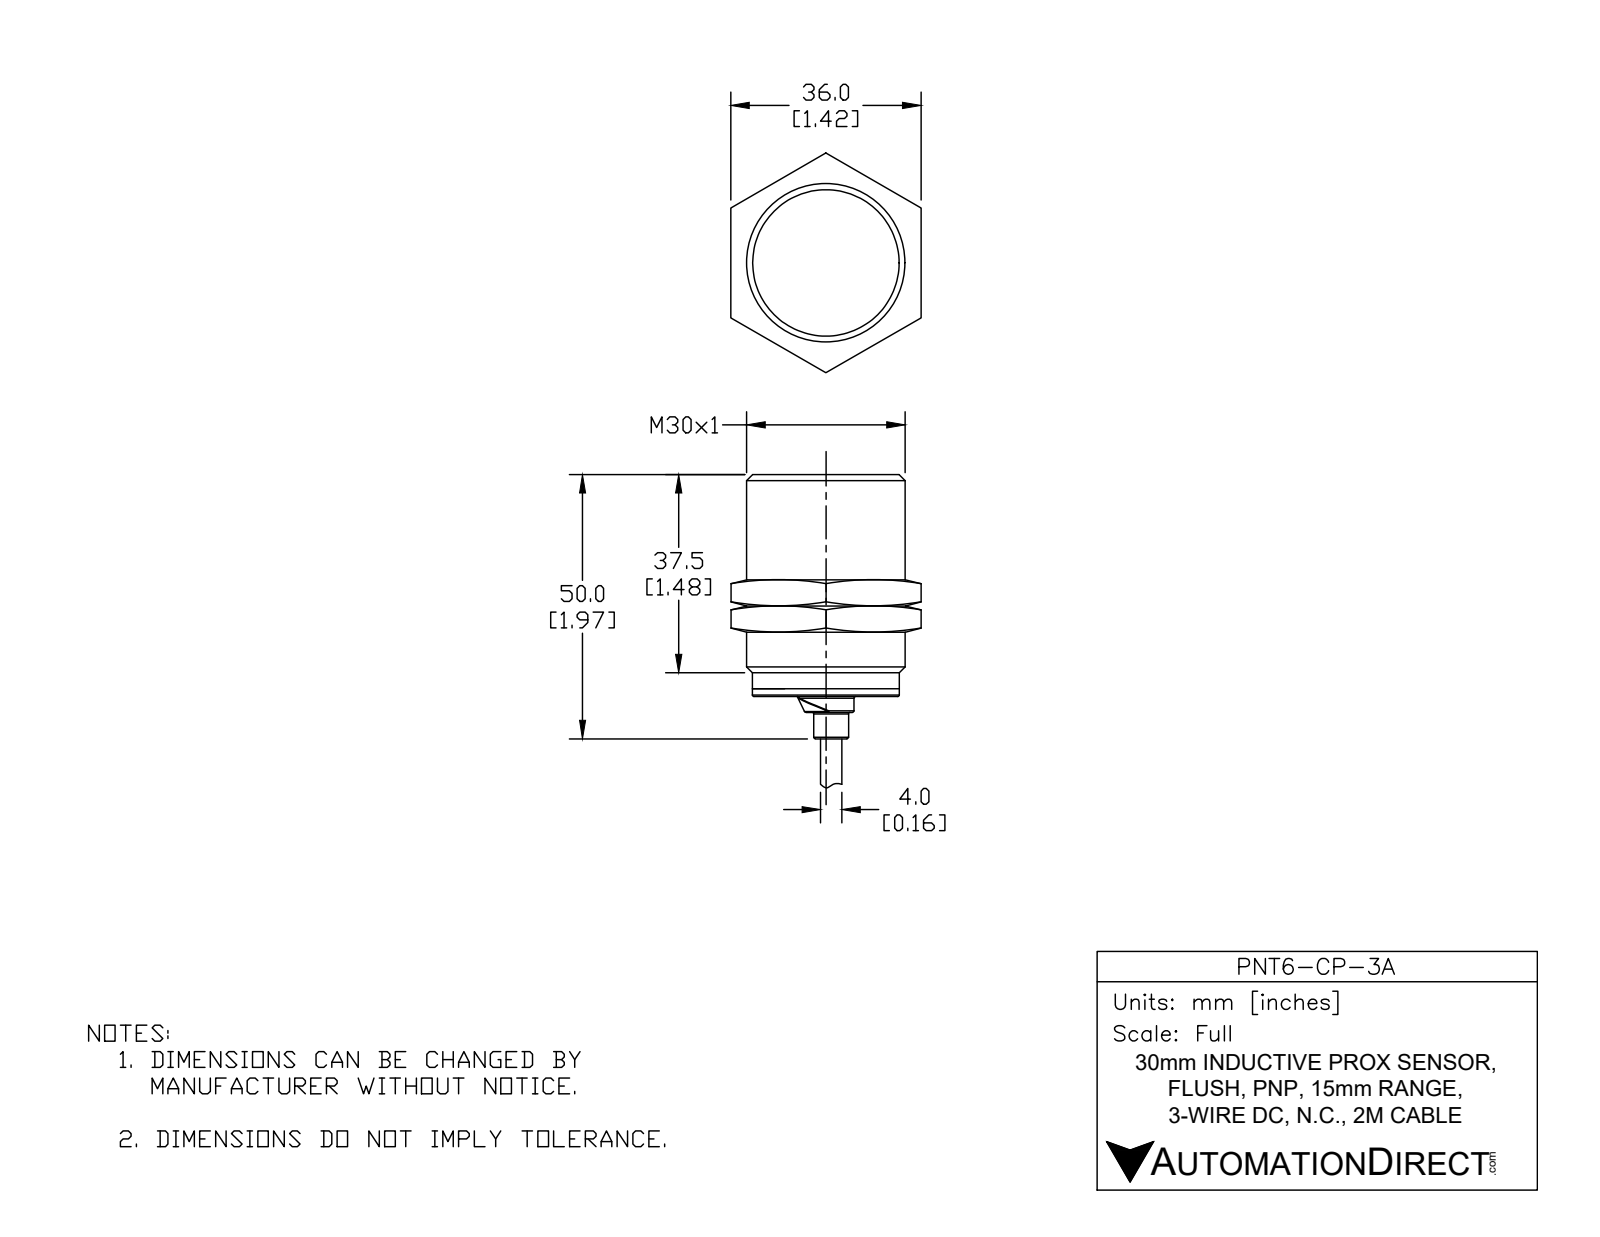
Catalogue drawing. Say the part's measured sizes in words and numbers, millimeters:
The part is named "PNT6-CP-3A". Its 3-D file was written by "SolidWorks 2017 (AUTOMOTIVE_DESIGN)". It is 1 solid with 77 faces: 15 planar, 30 cylindrical and 32 other. Overall it measures 100.8 by 30 by 30 millimeters. Its volume is 30 150 cubic millimeters and its surface area 6 268 square millimeters. Round holes: 1 of diameter 4.1. Round bosses or shafts: 6 of diameter 1.2, 1 of diameter 30, 1 of diameter 27.8, 1 of diameter 27.8, 1 of diameter 10.6, 1 of diameter 6.6, 1 of diameter 4. Partial cylindrical surfaces (rounded edges, fillets, slot ends): 1 of radius 2. The main face-to-face distances are 42, 45, 3, 50, 8, 5, 100.8, 58.8, 55.8, 50.8.
